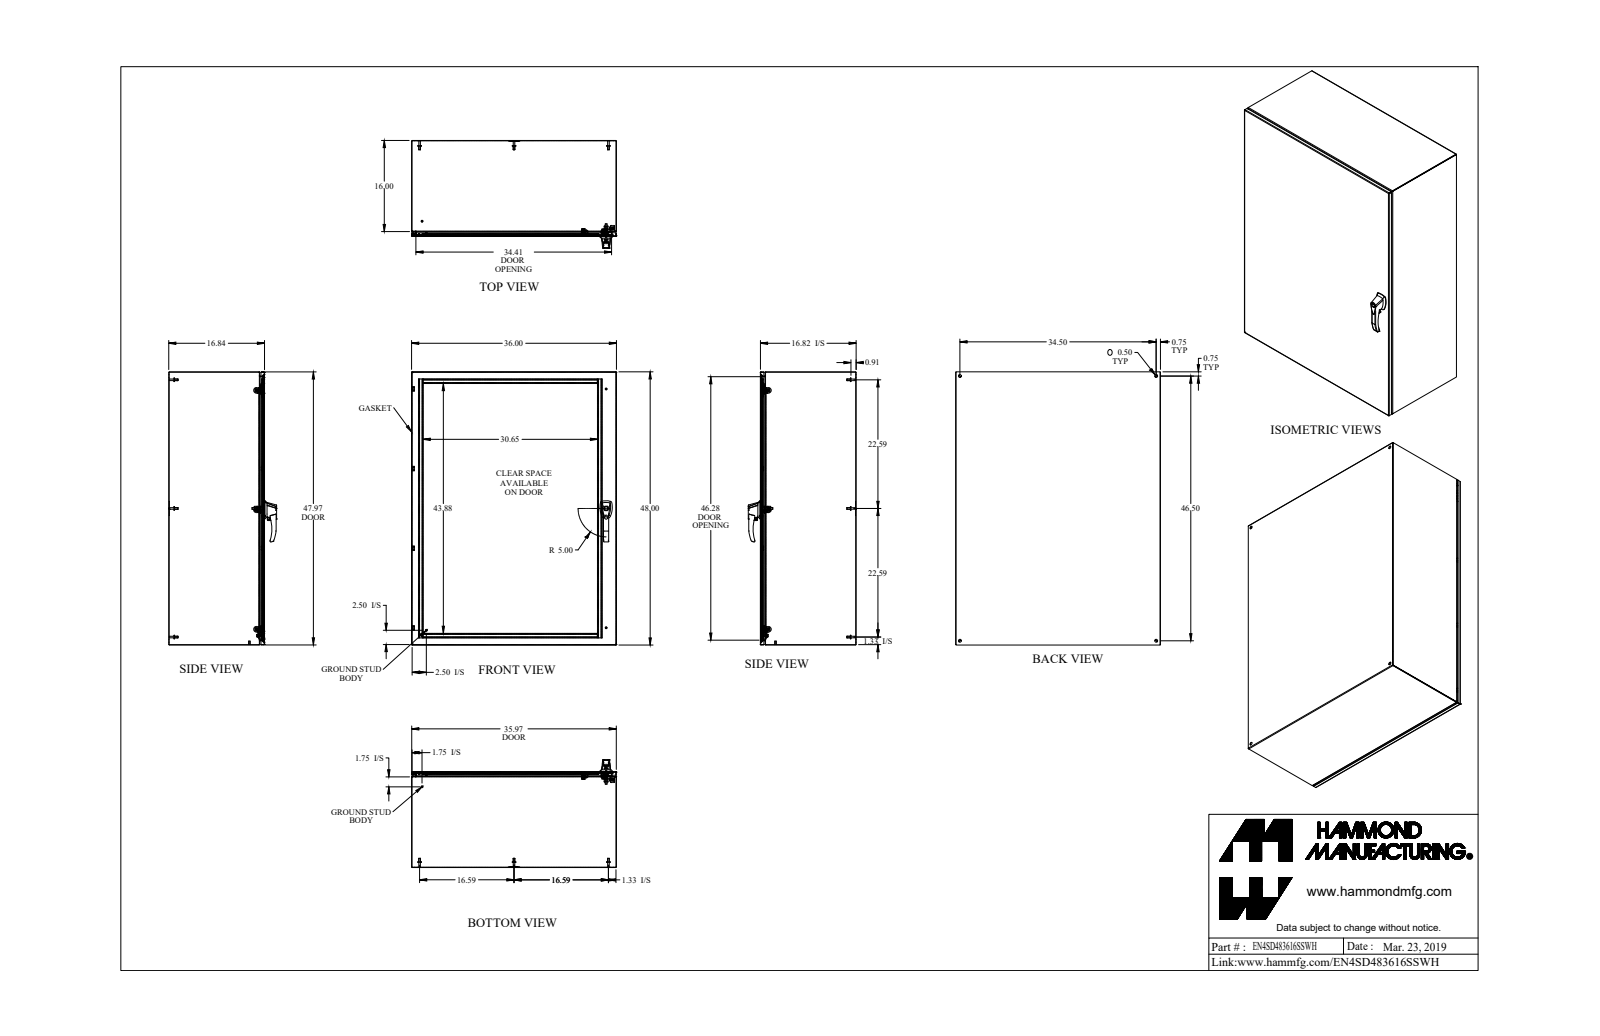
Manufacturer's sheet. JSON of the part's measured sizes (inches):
{"part_name": "EN4SD483616SSWH", "step_written_by": "SolidWorks 2018 (AUTOMOTIVE_DESIGN)", "units": "inches", "bodies": {"solids": 59, "faces": 1546, "planar": 677, "cylindrical": 590, "other": 279}, "overall_size": [48, 36, 18.958], "volume_in3": 510.9, "surface_area_in2": 14077, "round_holes": [[0.176, 6], [0.5, 4], [0.196, 3], [0.25, 3], [0.265, 3], [0.313, 3], [0.413, 3], [0.256, 2], [0.375, 2], [0.394, 2], [0.172, 1], [0.233, 1]], "round_bosses_or_shafts": [[0.313, 10], [0.625, 9], [0.275, 8], [0.25, 7], [0.375, 6], [0.156, 6], [1, 3], [0.51, 3]], "partial_cylinders_radius": [[0.048, 32], [0.01, 24], [0.036, 18], [0.108, 18], [0.062, 11], [0.094, 10], [0.016, 9], [0.125, 9]], "face_to_face_distances": [0.072, 16.771, 16.699, 16.843, 35.928, 35.856, 36, 0.072, 47.856, 47.928], "hole_center_spacings": [0.786, 41.969, 20.436, 20.984, 20.985, 21, 21.547, 23.274]}
